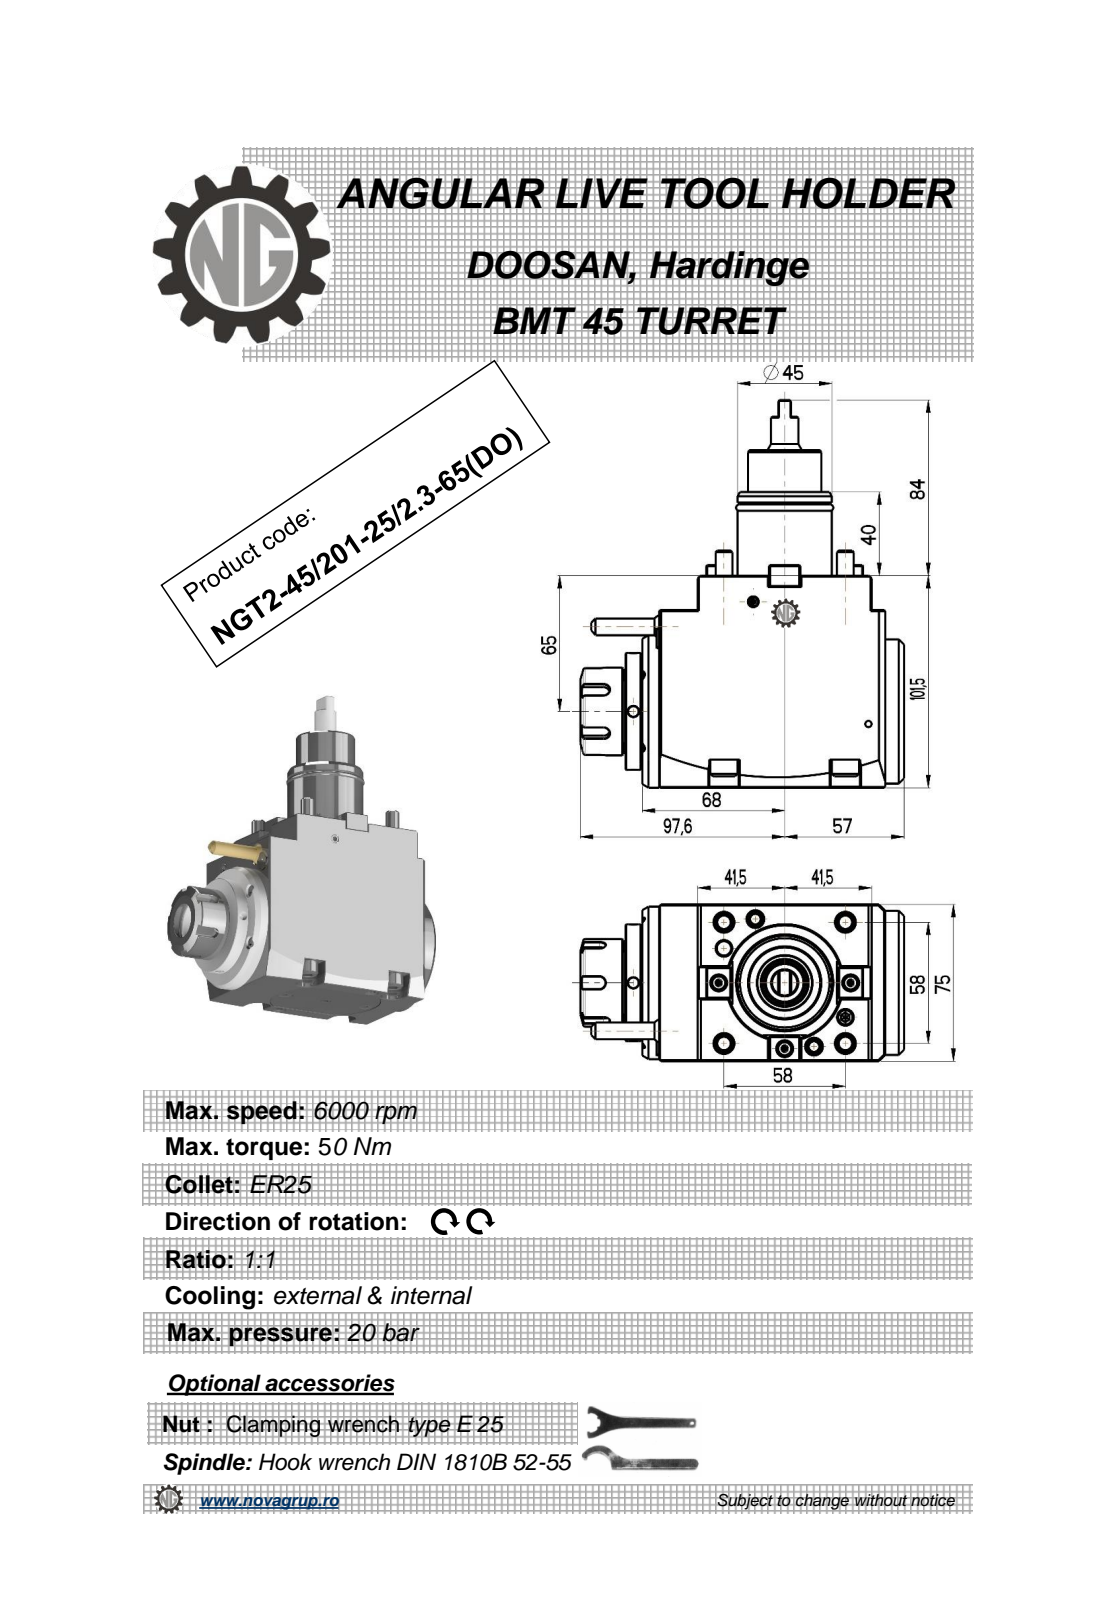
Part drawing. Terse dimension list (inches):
name: NGT2_45_201_25_1_3_65_DO
written by: PRO/ENGINEER BY PARAMETRIC TECHNOLOGY CORPORATION, 2010280 (CONFIG_CONTROL_DESIGN)
unit: in
bodies: 2 solids, 486 faces (231 planar, 111 cylindrical, 144 other)
size: 7.303 × 6.087 × 3.016
volume: 59.96 in³; area: 124 in²
holes: 3× ⌀0.197, 2× ⌀0.268, 1× ⌀0.118, 1× ⌀0.472, 1× ⌀0.799
bosses: 5× ⌀0.512, 5× ⌀0.315, 1× ⌀2.874, 1× ⌀2.717, 1× ⌀2.205, 1× ⌀1.772, 1× ⌀1.693, 1× ⌀1.654
rounds: 20× R0.01, 6× R0.008, 5× R0.118, 4× R0.276, 2× R0.01, 2× R0.031, 2× R21.654, 1× R0.098
face distances: 2.953, 3.996, 0.315, 0.354, 4.921, 4.567, 3.346, 4.252, 0.65, 4.606
hole spacings: 1.822, 1.834, 2.627, 4.039
